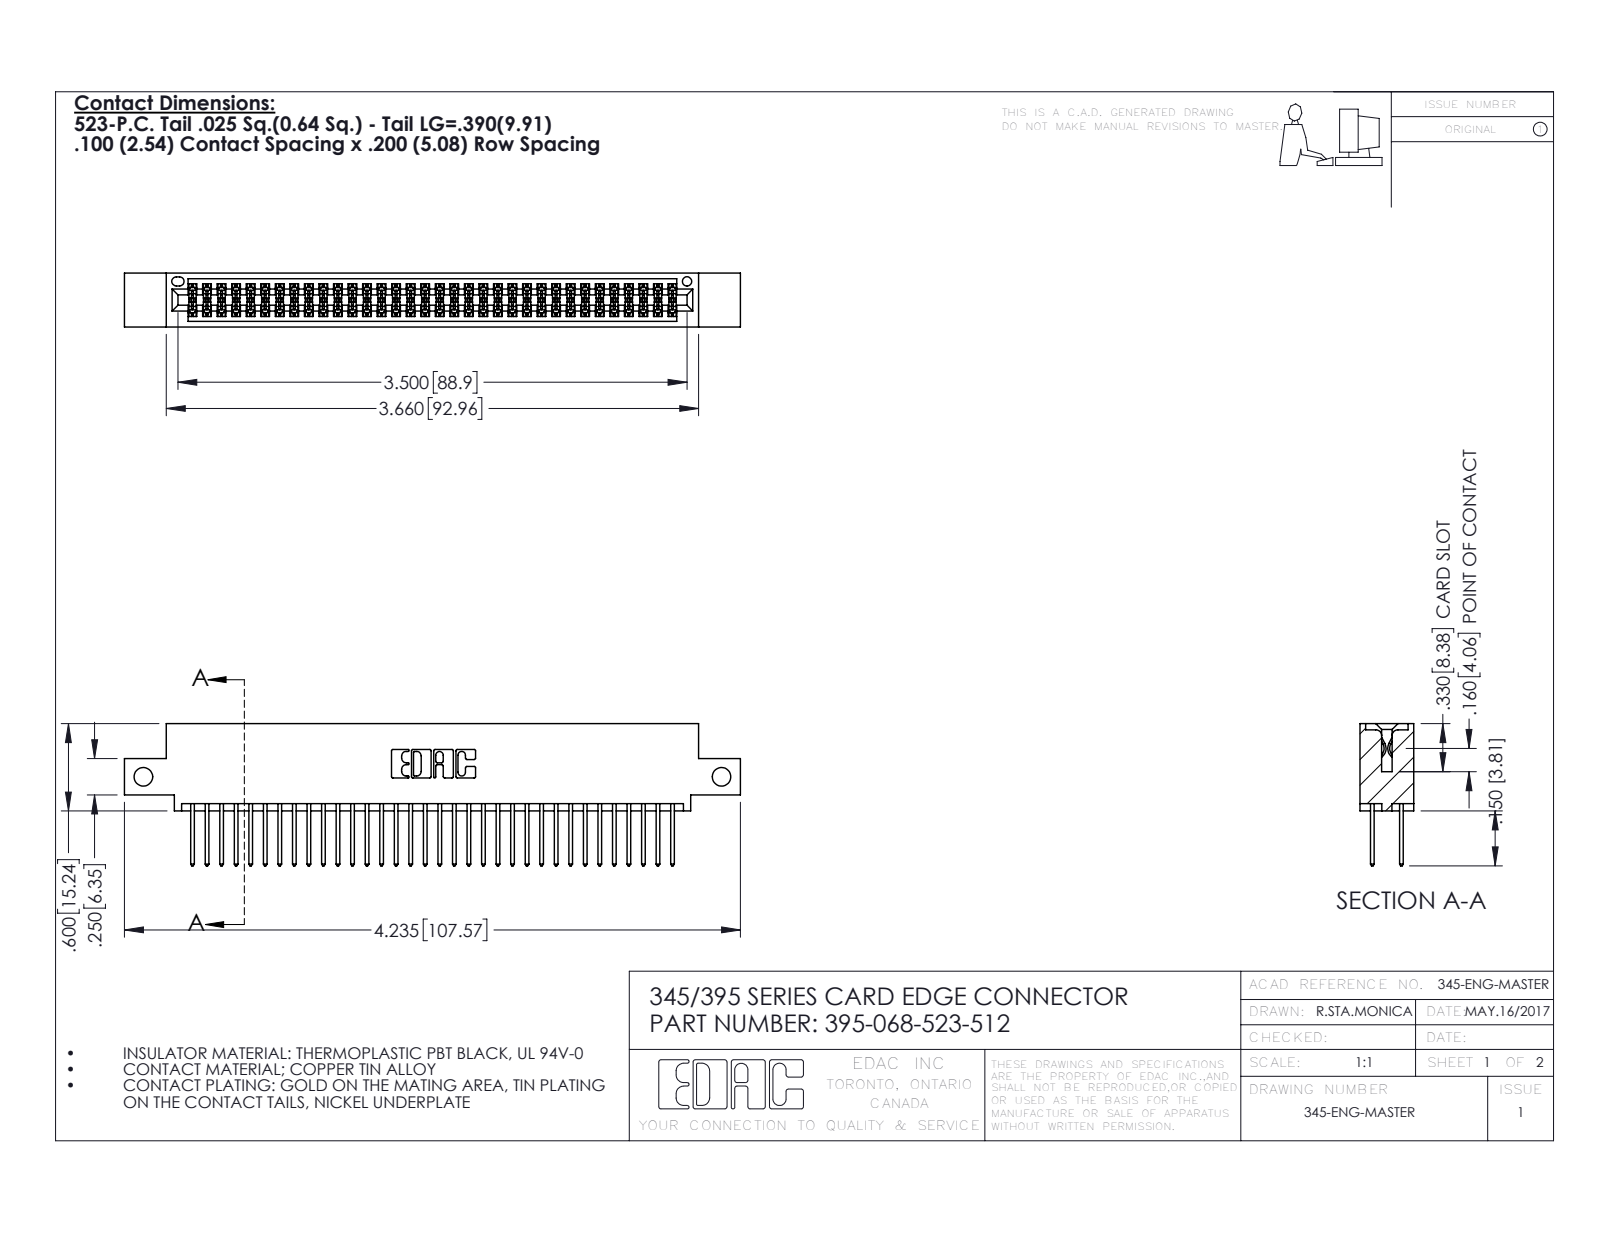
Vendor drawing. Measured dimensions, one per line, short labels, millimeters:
name: 345-292-001_345-293-123; 395-068-523-512; 345 Part_0.110 Offset - Side Mount
written by: SolidWorks 2016 (CONFIG_CONTROL_DESIGN)
unit: mm
bodies: 69 solids, 3530 faces (2328 planar, 1202 cylindrical, 0 other)
size: 107.6 × 24.8 × 9.4
volume: 10 400 mm³; area: 15 730 mm²
holes: 2× ⌀3.3, 1× ⌀1.6
rounds: 102× R0.2, 68× R0.3, 22× R0.3, 6× R0.2, 6× R0.8, 3× R0.7, 2× R0.4, 2× R0.5
face distances: 7.6, 1.8, 5.1, 2.5, 6.9, 0.6, 9.4, 5.7, 4.4, 3.8
hole spacings: 101
